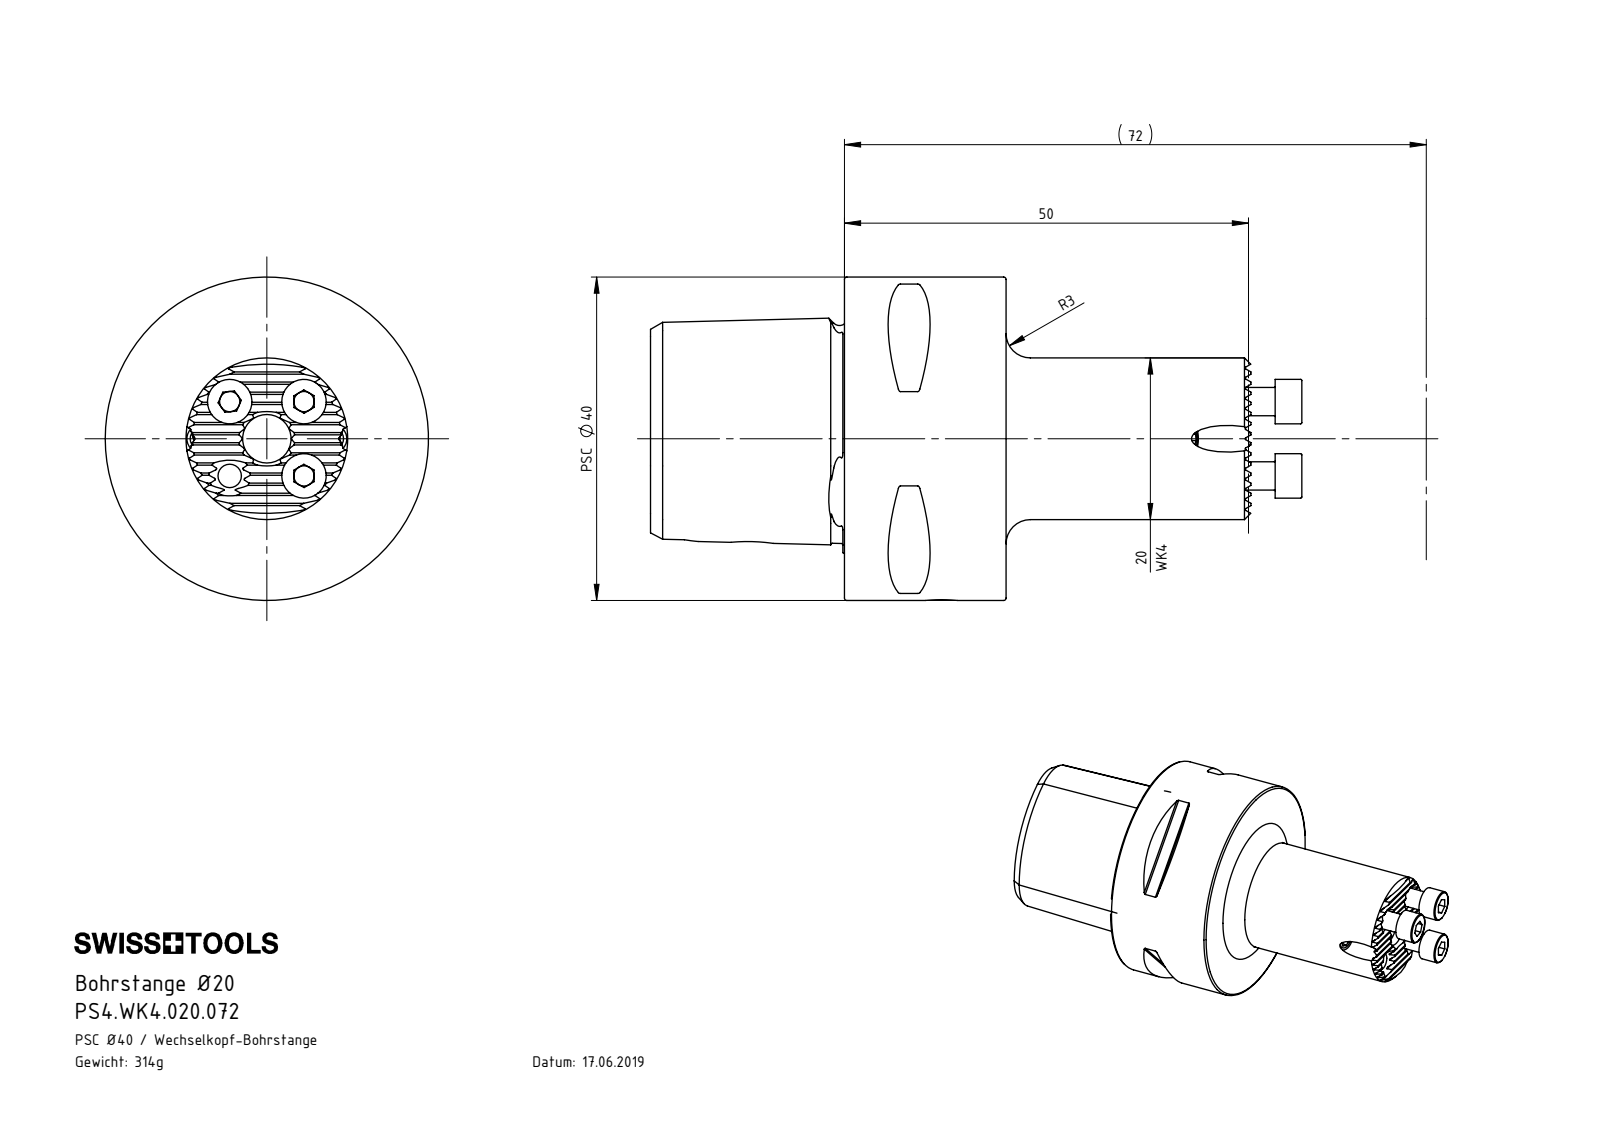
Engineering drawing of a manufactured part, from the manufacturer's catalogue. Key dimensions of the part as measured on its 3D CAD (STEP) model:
Part name (STEP PRODUCT): DIN 3771 - 6x1; PS4.WK4.020.072; PS4-WK4.020.072_C; ISO 4026 - M3 x 3 (+1 more)
STEP written by: SolidWorks 2017 (AUTOMOTIVE_DESIGN)
Units: millimetres
Bodies: 7 solids, 347 faces (184 planar, 73 cylindrical, 90 other)
Overall size (bounding box): 80.6 × 40 × 40
Volume: 40 032 mm³ · Surface area: 12 948 mm²
Round holes (diameter × count): ⌀2.5 ×5, ⌀2.9 ×4, ⌀3.3 ×2, ⌀4 ×1, ⌀4.6 ×1, ⌀6 ×1, ⌀6.8 ×1, ⌀7.4 ×1, ⌀12.5 ×1, ⌀18 ×1, ⌀20 ×1
Round bosses / shafts (diameter × count): ⌀5.5 ×3, ⌀3.5 ×3, ⌀3 ×2, ⌀40 ×1
Partial cylindrical surfaces — rounded edges, fillets, slot ends (radius × count): R0.12 ×15, R0.3 ×8, R3 ×1
Main face-to-face distances: 20, 24, 44, 4.33, 1.08, 3.25, 15.52, 5.41, 8.66, 2.17
Hole centre spacings: 6.51, 9.2, 13.01, 23.5
